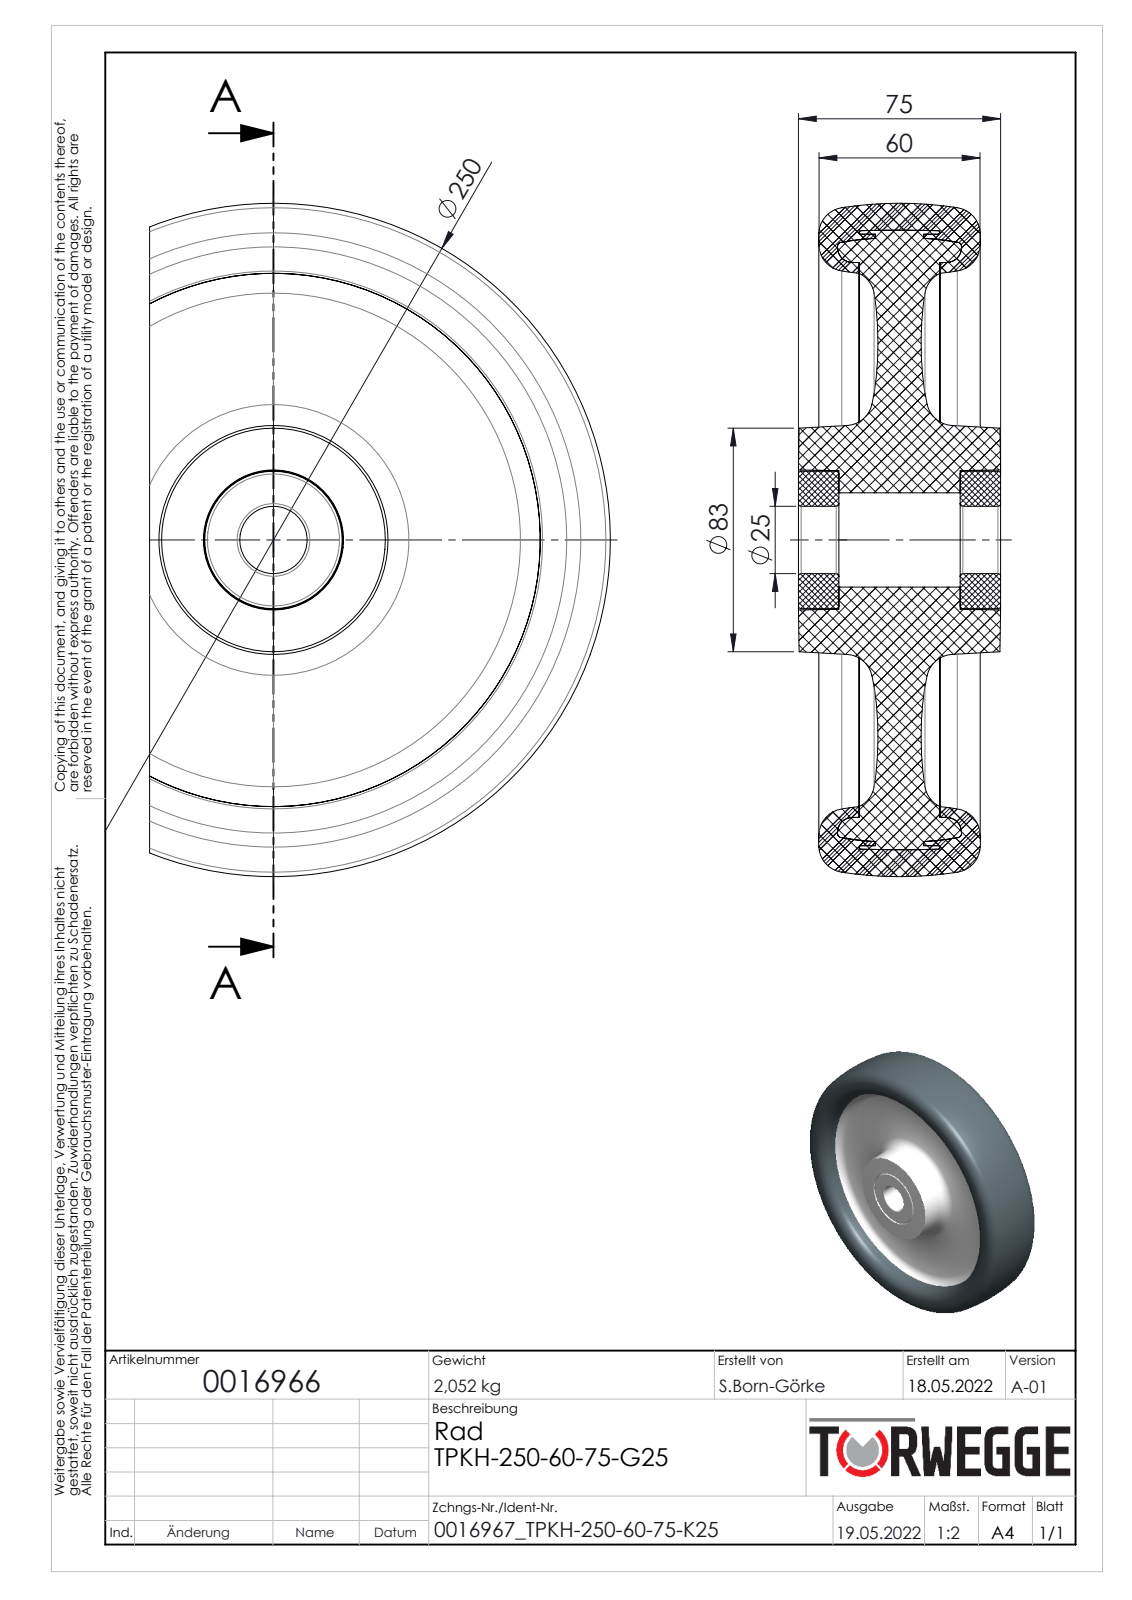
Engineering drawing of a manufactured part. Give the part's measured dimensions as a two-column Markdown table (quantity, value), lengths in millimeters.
| quantity | value |
| --- | --- |
| part name | 0016966 |
| STEP written by | SolidWorks 2020 (AUTOMOTIVE_DESIGN) |
| units | millimeters |
| bodies | 4 solids, 235 faces (76 planar, 40 cylindrical, 119 other) |
| overall size | 250 × 250 × 75 |
| volume | 1 818 000 mm³ |
| surface area | 332 014 mm² |
| round holes (diameter × count) | 25 × 1, 35 × 1, 227 × 1 |
| round bosses / shafts (diameter × count) | 51 × 1 |
| partial cylindrical surfaces (radius × count) | 112 × 1 |
| main face-to-face distances | 30, 7.5, 37.5, 13.5, 31.5, 6, 24, 15, 22.5, 28.5 |
